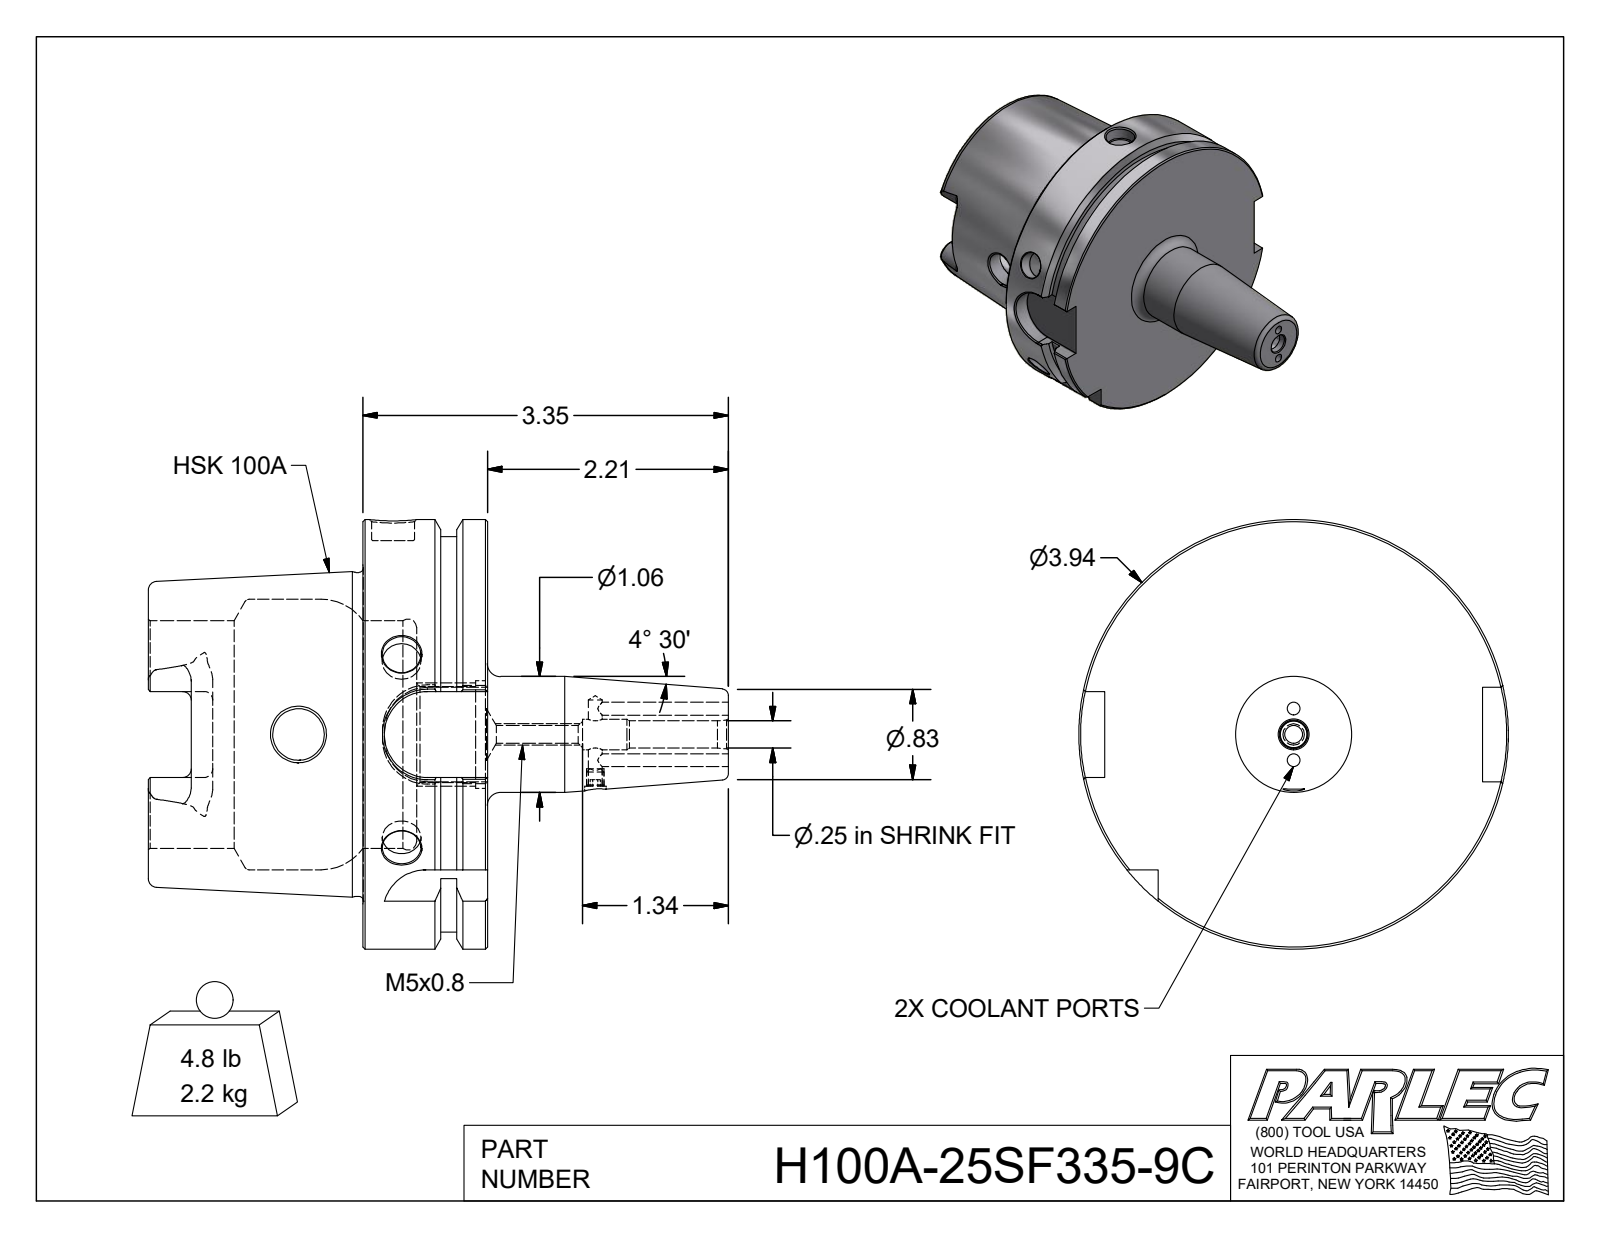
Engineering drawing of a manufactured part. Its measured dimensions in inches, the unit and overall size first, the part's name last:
Units: inches
Overall size (bounding box): 5.319 × 3.937 × 3.937
Round holes (diameter × count): ⌀0.118 ×2, ⌀0.354 ×2, ⌀0.128 ×1, ⌀0.163 ×1, ⌀0.197 ×1, ⌀0.25 ×1, ⌀0.28 ×1, ⌀0.394 ×1, ⌀0.472 ×1, ⌀0.472 ×1, ⌀0.881 ×1, ⌀0.985 ×1
Round bosses / shafts (diameter × count): ⌀3.937 ×1, ⌀3.622 ×1, ⌀2.967 ×1, ⌀1.063 ×1
Partial cylindrical surfaces — rounded edges, fillets, slot ends (radius × count): R0.079 ×6, R0.192 ×4, R0.394 ×4
Main face-to-face distances: 1.142, 0.492, 0.65, 1.969, 2.461, 3.11, 3.465, 2.83, 0.861, 0.369
Hole centre spacings: 0.236, 0.472, 1.854
Volume: 17.06 in³ · Surface area: 86.36 in²
Bodies: 1 solid, 150 faces (49 planar, 42 cylindrical, 59 other)
STEP written by: Autodesk Inventor 2018 (AUTOMOTIVE_DESIGN)
